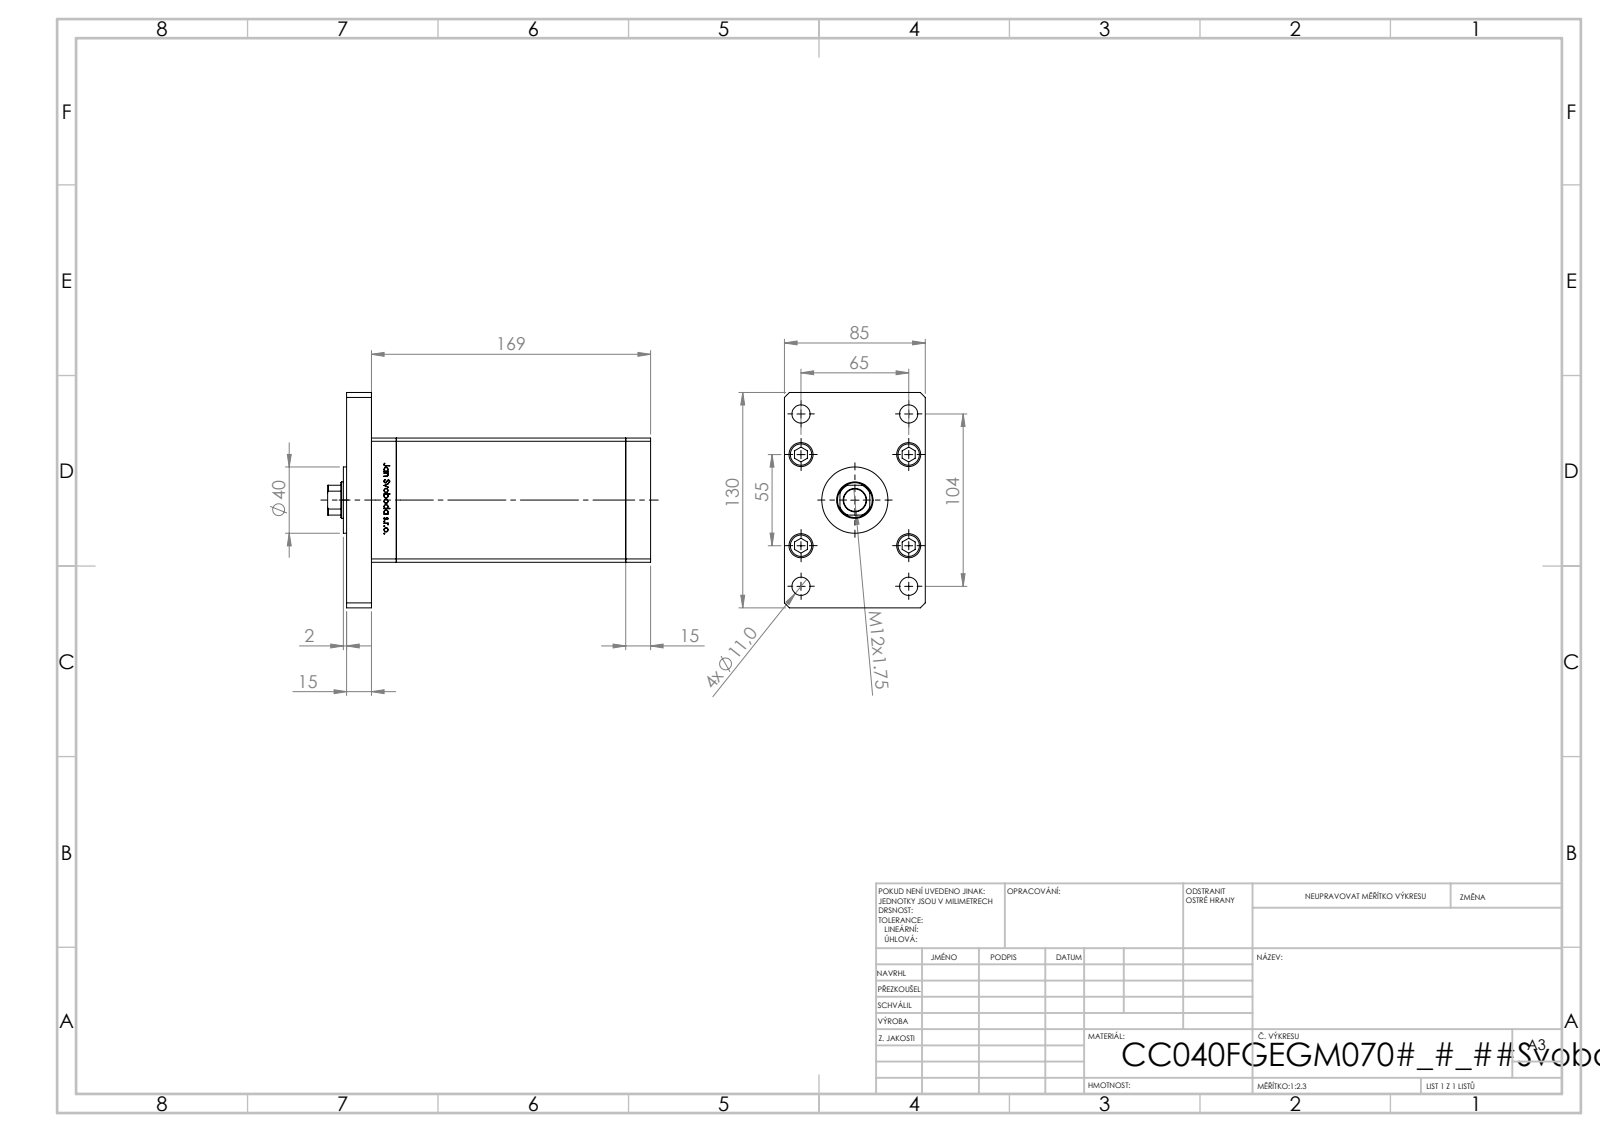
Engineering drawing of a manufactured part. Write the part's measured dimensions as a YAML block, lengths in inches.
part_name: "V220C BACK_F; ALLEN BOLT; V220C_F; V220C_F_MIDDLE (+2 more)"
step_written_by: "SolidWorks 2019 (CONFIG_CONTROL_DESIGN)"
units: inches
bodies: {solids: 19, faces: 1310, planar: 517, cylindrical: 187, other: 606}
overall_size: [7.677, 5.118, 3.346]
volume: 67.86
surface_area: 300
round_holes:
  - {diameter: 0.433, count: 9}
  - {diameter: 0.61, count: 5}
  - {diameter: 0.394, count: 4}
  - {diameter: 0.571, count: 4}
  - {diameter: 0.079, count: 2}
  - {diameter: 0.518, count: 2}
  - {diameter: 0.531, count: 1}
  - {diameter: 0.866, count: 1}
  - {diameter: 0.925, count: 1}
round_bosses_or_shafts:
  - {diameter: 0.315, count: 9}
  - {diameter: 0.571, count: 5}
  - {diameter: 1.575, count: 1}
partial_cylinders:
  - {radius: 0.037, count: 2}
  - {radius: 0.413, count: 1}
face_to_face_distances: [0.591, 3.346, 6.043, 6.634, 2.953, 1.181, 5.453, 7.224, 0.413, 1.083]
hole_center_spacings: [1.102, 0.965, 1.676, 2.414, 2.559, 2.735, 3.13, 4.043]
